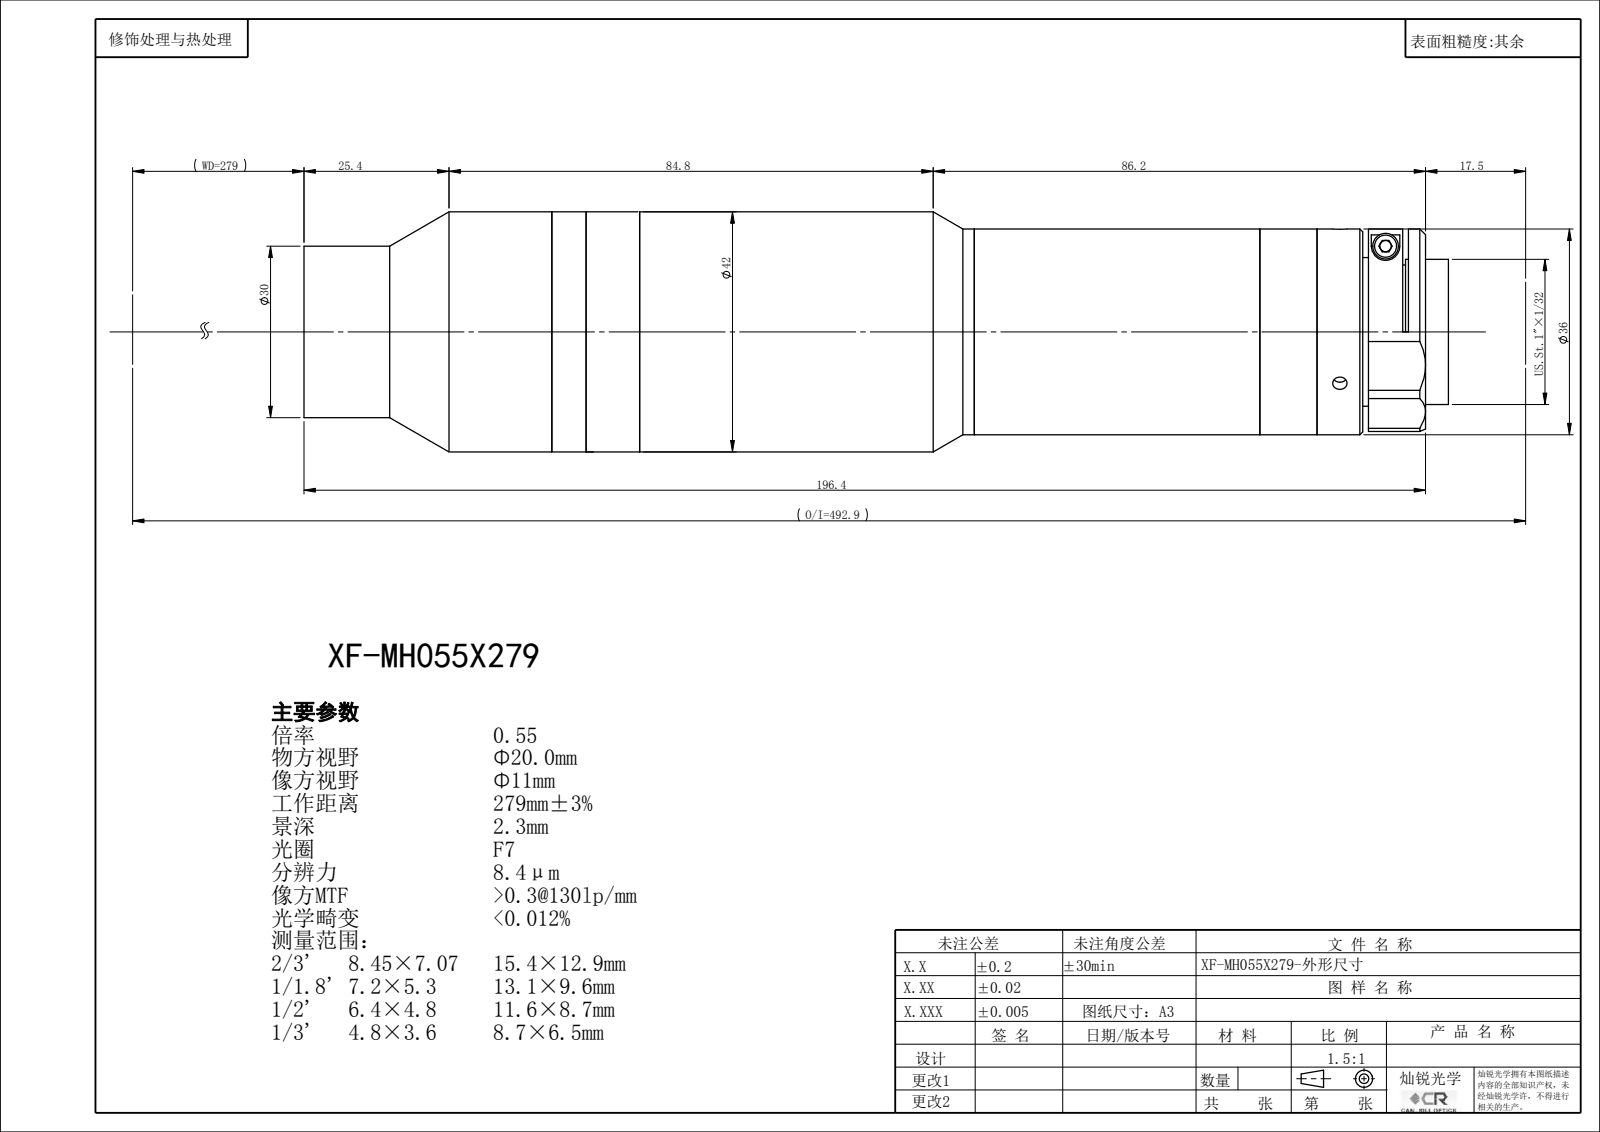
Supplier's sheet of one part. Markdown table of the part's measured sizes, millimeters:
| quantity | value |
| --- | --- |
| part name | XF-MH055X279 |
| STEP written by | SolidWorks 2022 (CONFIG_CONTROL_DESIGN) |
| units | millimeters |
| bodies | 0 solids, 134 faces (66 planar, 44 cylindrical, 24 other) |
| overall size | 200.19 × 42 × 42 |
| round holes (diameter × count) | 2.5 × 3, 22.4 × 1, 24 × 1, 26.4 × 1 |
| round bosses / shafts (diameter × count) | 42 × 1, 36 × 1, 34 × 1, 30 × 1, 25.4 × 1 |
| main face-to-face distances | 1.5, 27.34, 28.84, 50, 77.34, 78.84, 66, 16, 11.34, 12.84 |
